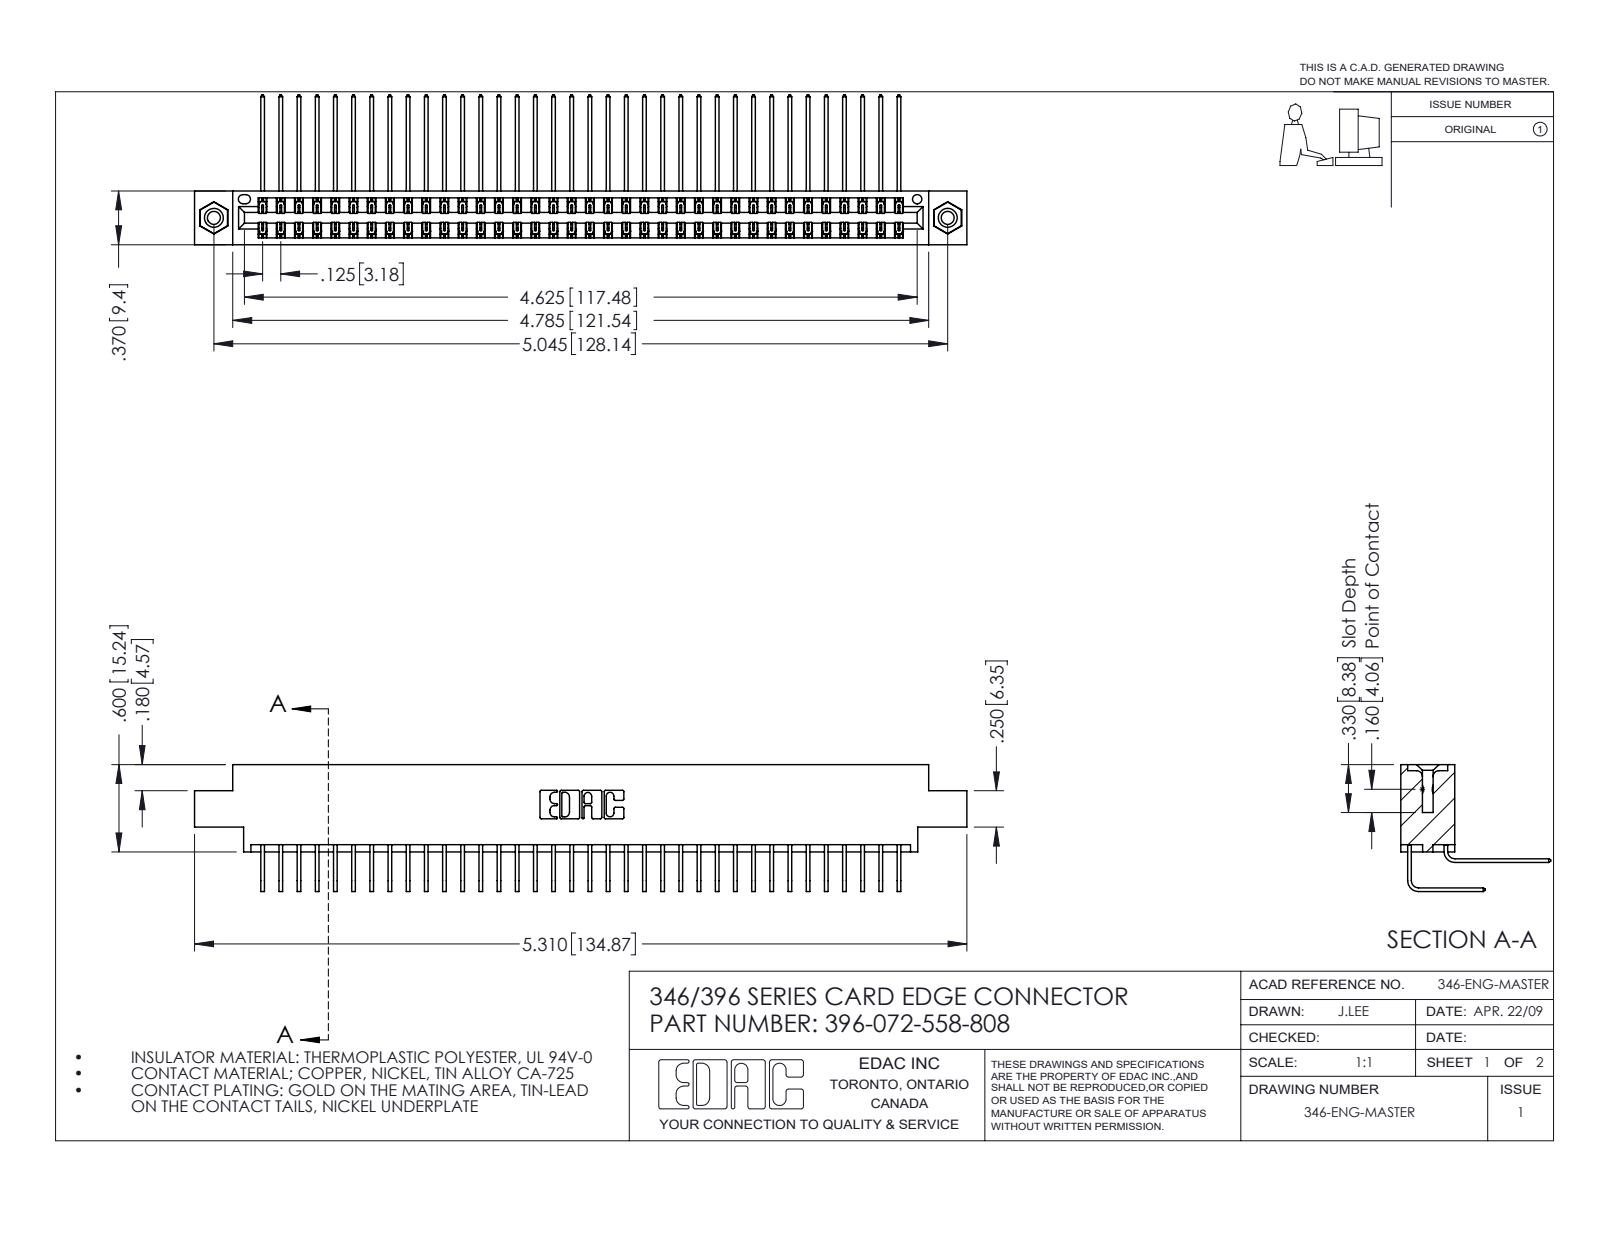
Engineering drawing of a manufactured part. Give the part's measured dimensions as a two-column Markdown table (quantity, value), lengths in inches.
| quantity | value |
| --- | --- |
| part name | 346 Part_0.170 Offset - 0.156 Dia-TI; 345-292-001_558 559 Tail - 1; 345-250-001_345-250-003-102; 345-292-001_558 Tail - 2 (+1 more) |
| STEP written by | SolidWorks 2016 (CONFIG_CONTROL_DESIGN) |
| units | inches |
| bodies | 75 solids, 4074 faces (2776 planar, 1282 cylindrical, 16 other) |
| overall size | 5.31 × 1.03 × 0.873 |
| volume | 0.815 in³ |
| surface area | 31.72 in² |
| round holes (diameter × count) | 0.089 × 2, 0.125 × 2, 0.156 × 2, 0.064 × 1 |
| round bosses / shafts (diameter × count) | 0.155 × 2 |
| partial cylindrical surfaces (radius × count) | 0.006 × 108, 0.01 × 22, 0.007 × 6, 0.031 × 6, 0.026 × 3, 0.014 × 2, 0.022 × 2, 0.024 × 2 |
| main face-to-face distances | 0.322, 0.048, 0.025, 0.37, 0.25, 0.298, 0.072, 0.275, 0.222, 0.148 |
| hole center spacings | 0.246, 4.836, 5.045 |
